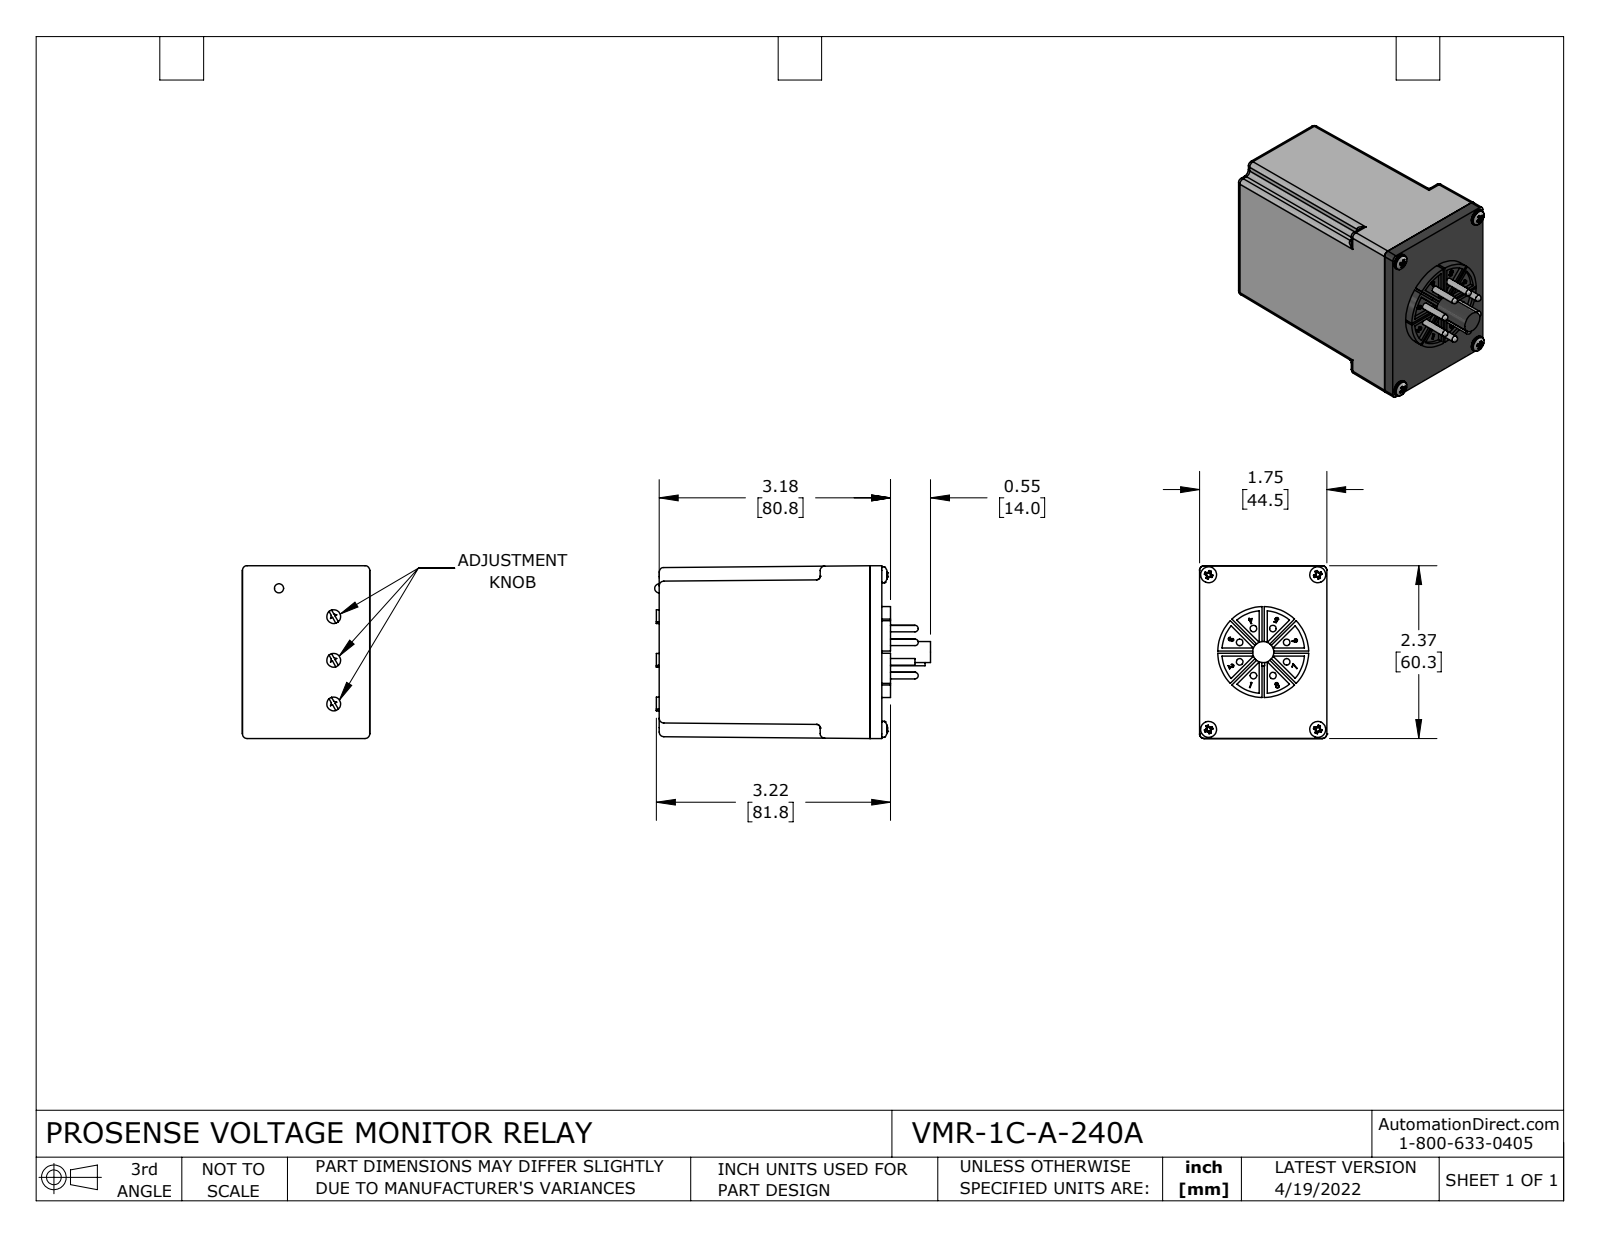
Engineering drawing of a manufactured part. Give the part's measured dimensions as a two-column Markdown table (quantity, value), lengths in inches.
| quantity | value |
| --- | --- |
| part name | VMR-1C-A-240A |
| STEP written by | SolidWorks 2021 (CONFIG_CONTROL_DESIGN) |
| units | inches |
| bodies | 18 solids, 574 faces (249 planar, 170 cylindrical, 155 other) |
| overall size | 3.79 × 2.375 × 1.75 |
| volume | 12.25 in³ |
| surface area | 44.71 in² |
| round holes (diameter × count) | 0.125 × 4 |
| round bosses / shafts (diameter × count) | 0.09 × 8, 0.219 × 4, 0.19 × 3, 1.25 × 1, 0.29 × 1 |
| partial cylindrical surfaces (radius × count) | 0.063 × 32, 0.005 × 8, 0.05 × 4, 0.57 × 1 |
| main face-to-face distances | 2.9, 0.16, 3.06, 0.07, 0.23, 3.13, 0.188, 0.05, 0.12, 0.28 |
| hole center spacings | 1.5, 2.125, 2.601 |
